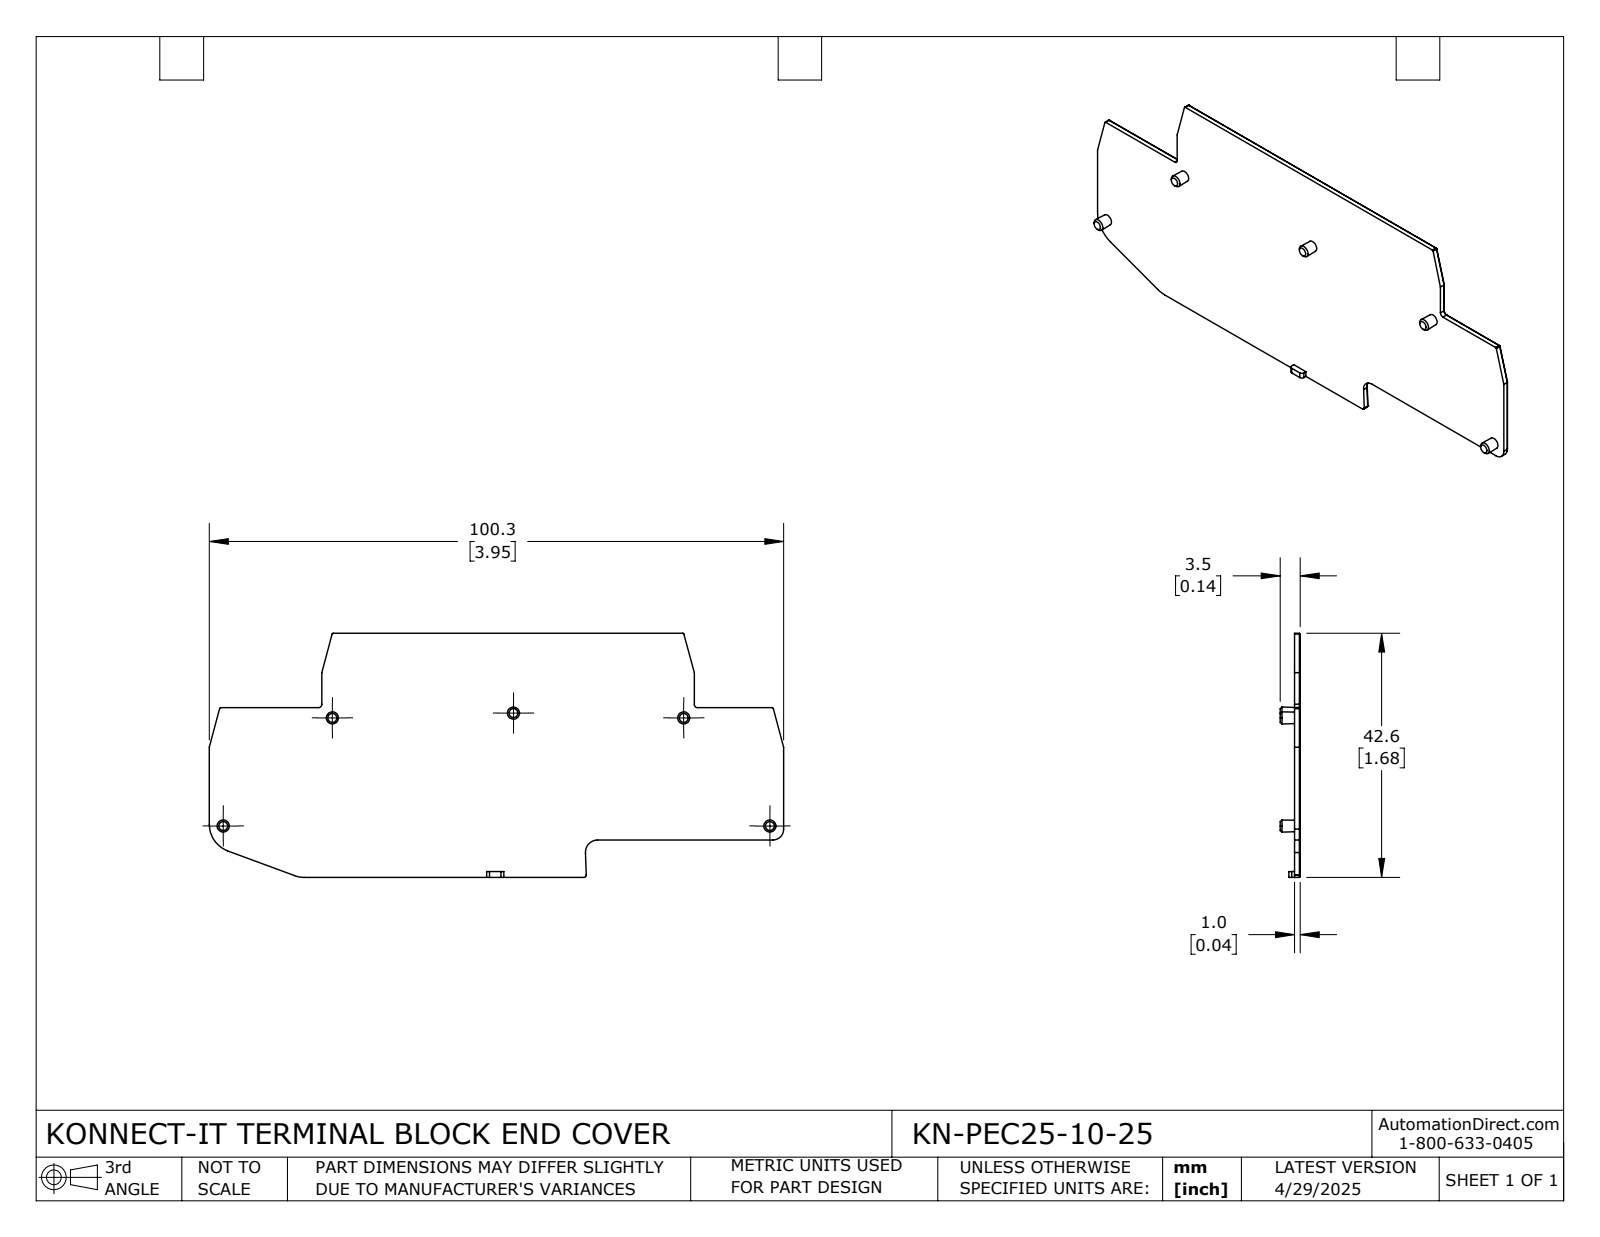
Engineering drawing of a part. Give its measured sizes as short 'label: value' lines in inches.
name: KN-PEC25-10-25
written by: SolidWorks 2024 (CONFIG_CONTROL_DESIGN)
unit: in
bodies: 1 solid, 92 faces (44 planar, 28 cylindrical, 20 other)
size: 3.949 × 1.678 × 0.138
volume: 0.217 in³; area: 11.46 in²
rounds: 4× R0.004, 4× R0.008, 2× R0.02, 2× R0.024, 2× R0.028, 2× R0.189, 2× R0.193, 1× R0.012
face distances: 0.039, 1.678, 0.256, 0.512, 0.033, 1.422, 1.166, 0.909, 1.674, 1.418
